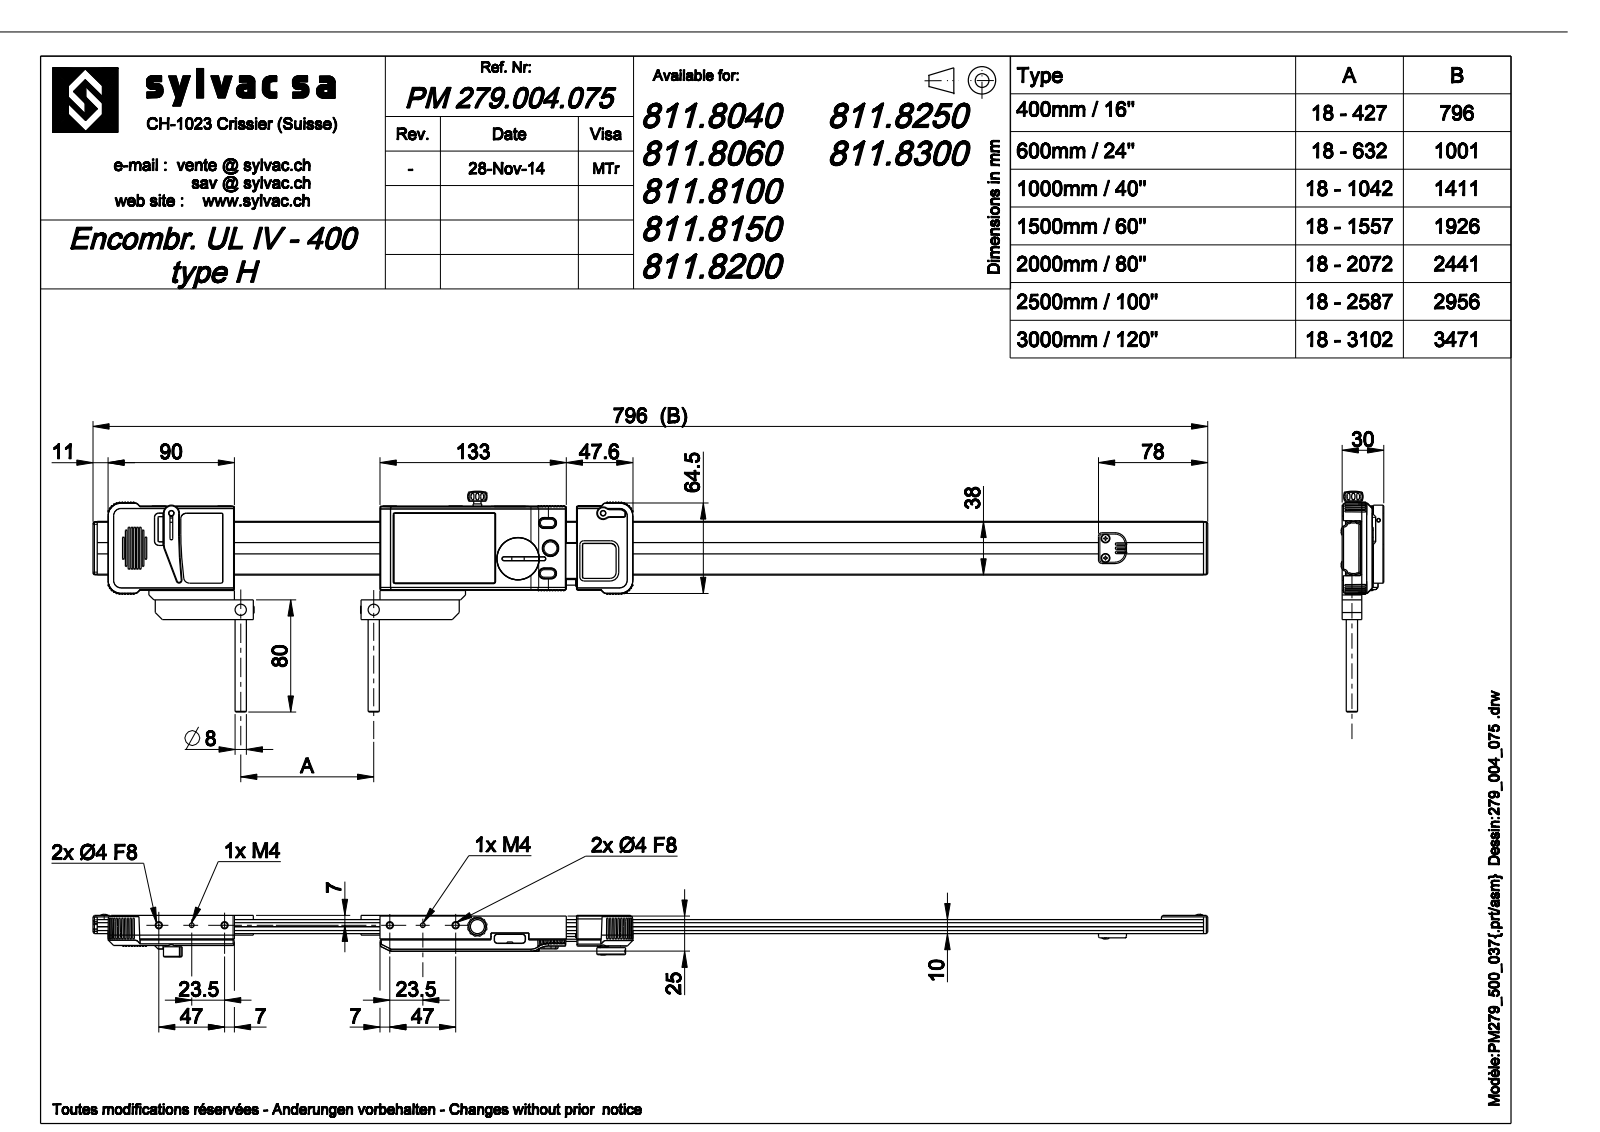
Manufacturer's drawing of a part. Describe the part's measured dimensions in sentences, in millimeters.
The part is named "PM279_500_037_SW0001". Its 3-D file was written by "PRO/ENGINEER BY PARAMETRIC TECHNOLOGY CORPORATION, 2009380 (CONFIG_CONTROL_DESIGN)". It is 0 solids with 826 faces: 335 planar, 170 cylindrical and 321 other. Overall it measures 796 by 157.63 by 30.52 millimeters. Round holes: 3 of diameter 4.02, 2 of diameter 8, 1 of diameter 15. Round bosses or shafts: 2 of diameter 8, 1 of diameter 5.2, 1 of diameter 4. Partial cylindrical surfaces (rounded edges, fillets, slot ends): 30 of radius 0.3, 19 of radius 2, 12 of radius 1, 12 of radius 1.5, 9 of radius 0.6, 5 of radius 5, 5 of radius 10, 4 of radius 0.75. The main face-to-face distances are 10, 1, 3, 9, 13, 4, 8, 12, 11.5, 3.3. The hole center spacings are 47, 95, 118, 165, 579.17, 673.93.
